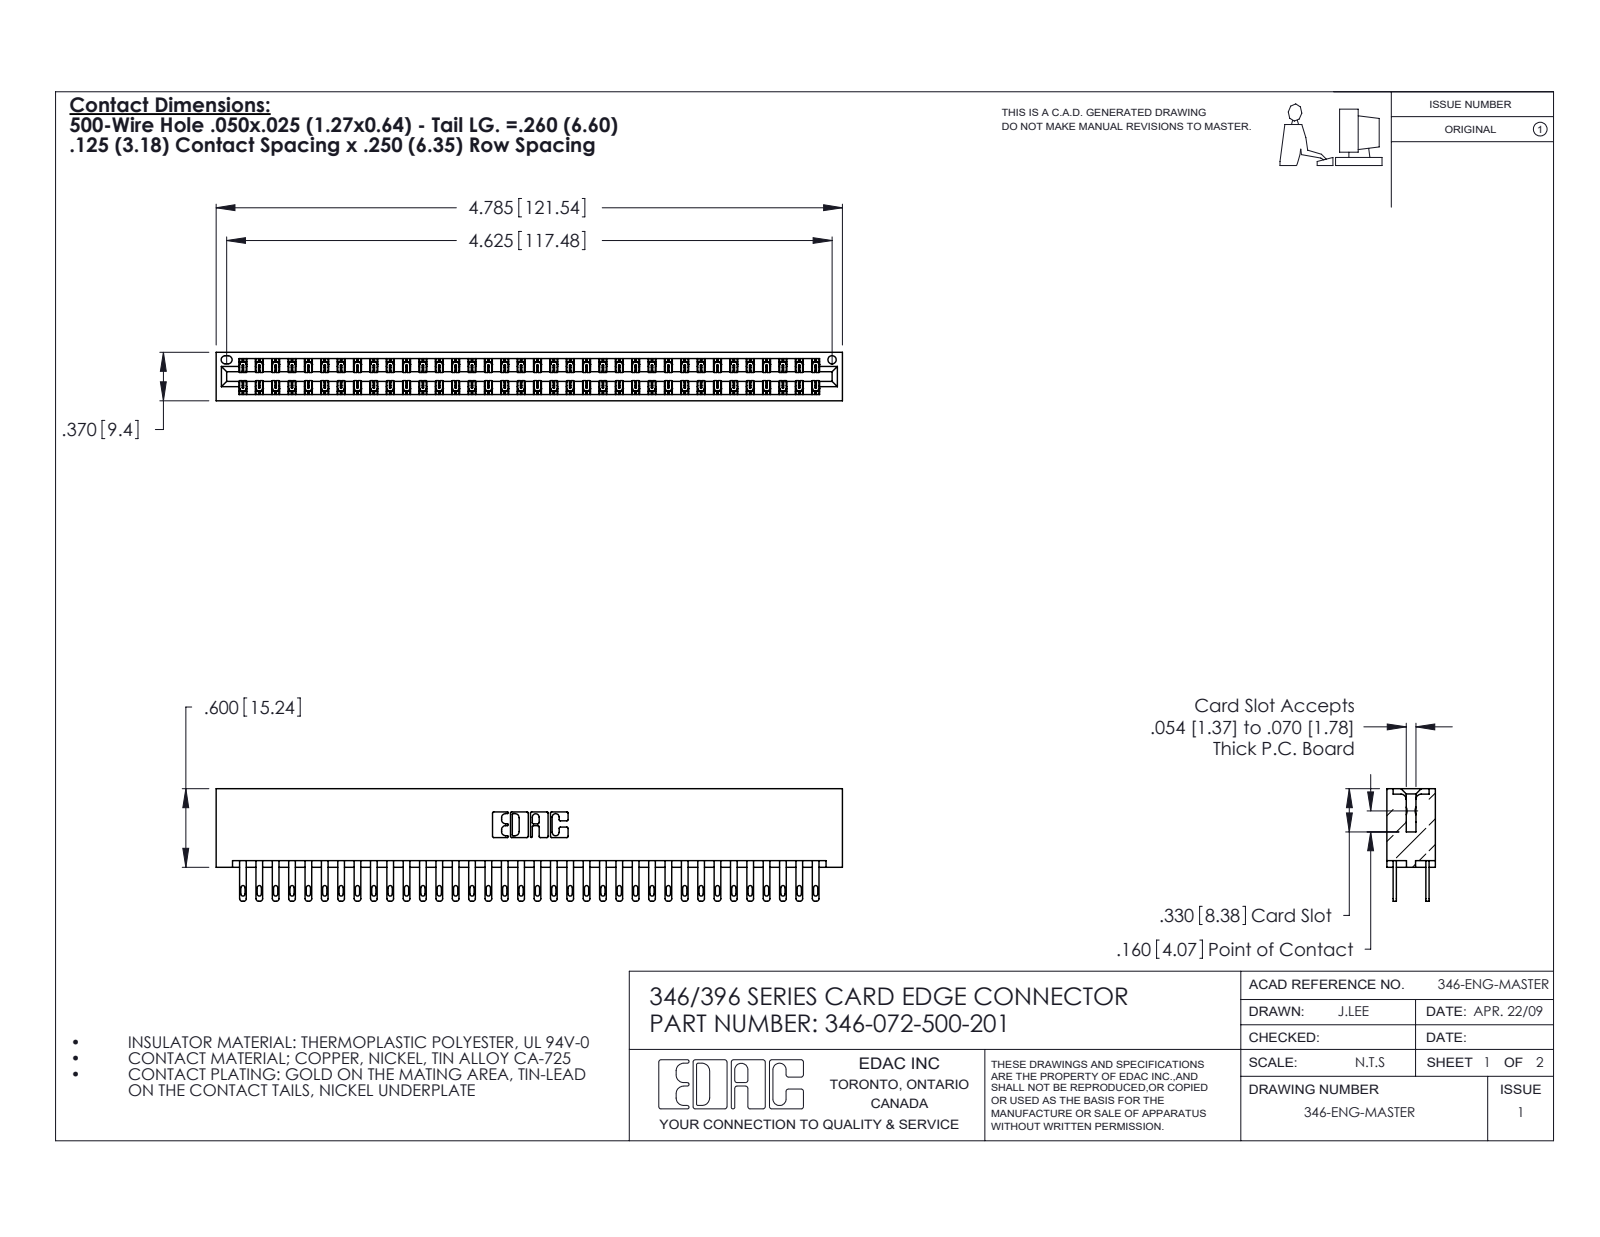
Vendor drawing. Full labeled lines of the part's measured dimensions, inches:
Part name (STEP PRODUCT): 346-072-500-201; 346 Part_No Mounting Lugs; 345-292-001_345-293-100
STEP written by: SolidWorks 2020 (CONFIG_CONTROL_DESIGN)
Units: inches
Bodies: 73 solids, 3570 faces (2160 planar, 1410 cylindrical, 0 other)
Overall size (bounding box): 4.785 × 0.86 × 0.37
Volume: 0.769 in³ · Surface area: 28.12 in²
Round holes (diameter × count): ⌀0.064 ×1
Partial cylindrical surfaces — rounded edges, fillets, slot ends (radius × count): R0.006 ×108, R0.016 ×72, R0.02 ×72, R0.01 ×22, R0.007 ×6, R0.031 ×6, R0.026 ×3, R0.014 ×2
Main face-to-face distances: 0.048, 0.322, 0.25, 0.072, 0.298, 0.025, 0.37, 0.275, 0.148, 0.222
